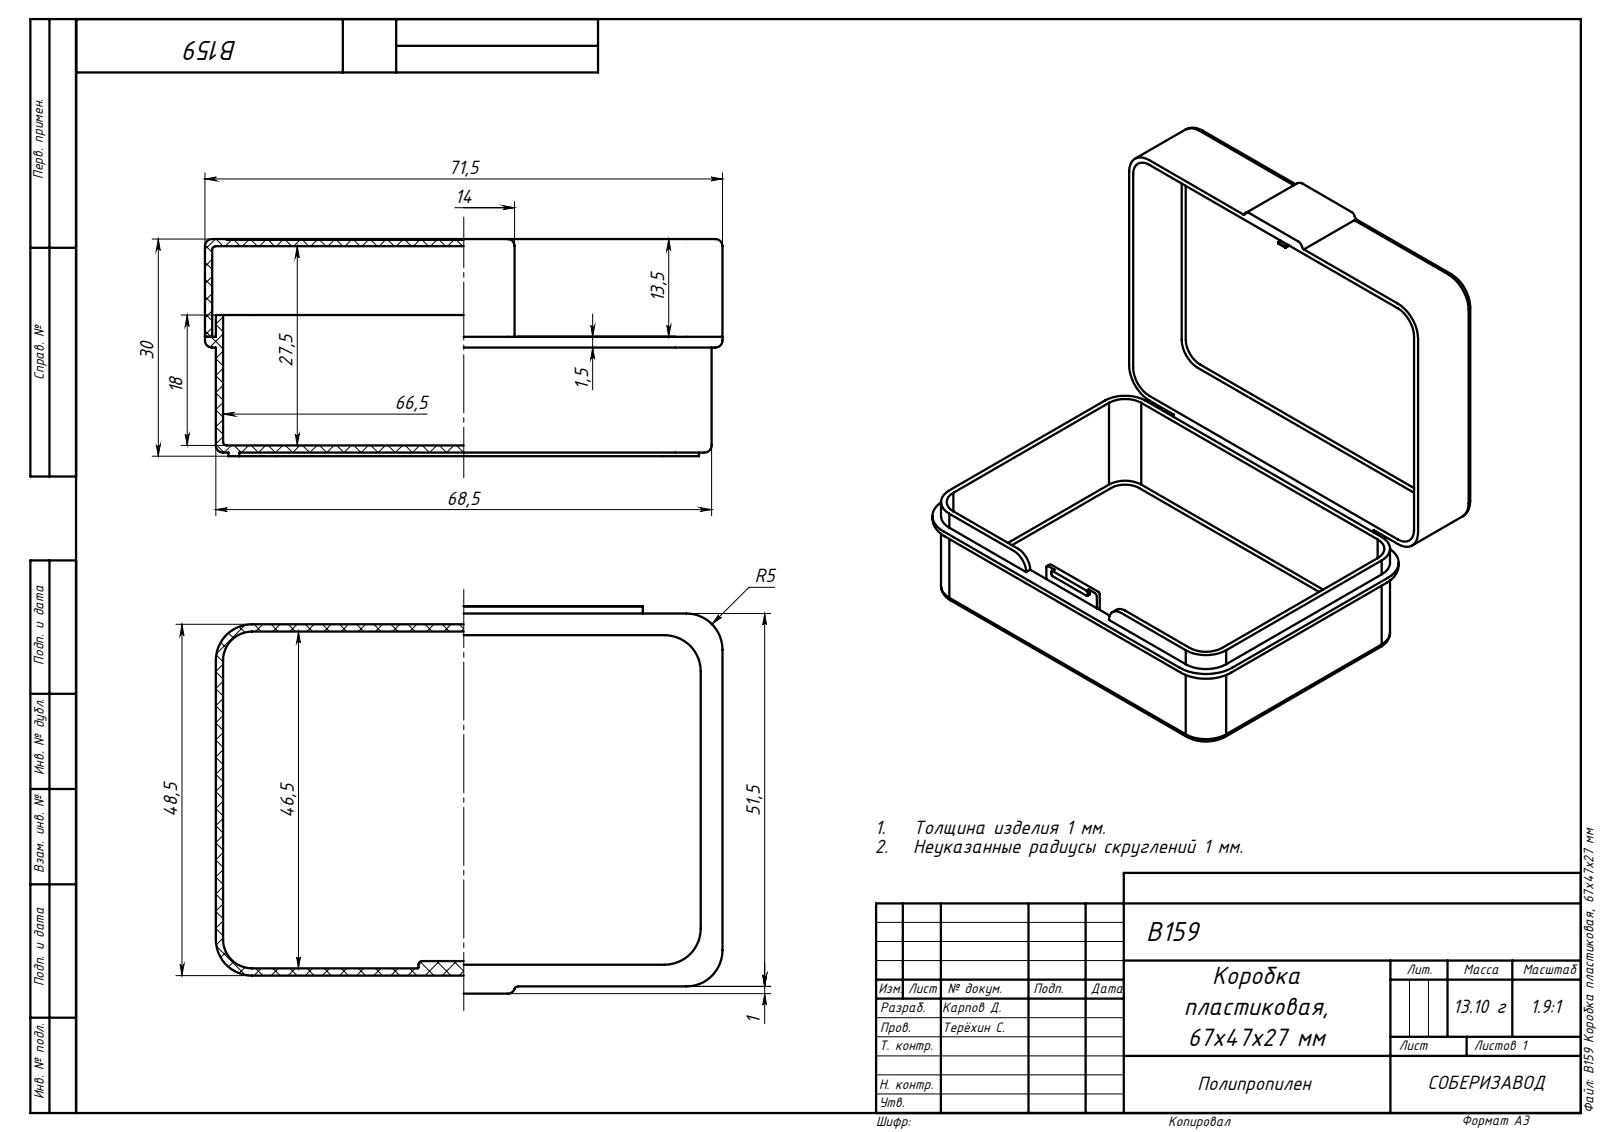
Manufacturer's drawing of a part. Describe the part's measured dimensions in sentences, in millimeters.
The part is named "B159 Емкость; B159 Крышка; B159 Коробка пластиковая, 67x47x27 мм". Its 3-D file was written by "SolidWorks 2020 (AUTOMOTIVE_DESIGN)". It is 2 solids with 193 faces: 78 planar, 85 cylindrical and 30 other. Overall it measures 71.5 by 53.5 by 30 millimeters. Its volume is 14 569 cubic millimeters and its surface area 29 026 square millimeters. Partial cylindrical surfaces (rounded edges, fillets, slot ends): 20 of radius 5, 15 of radius 0.5, 15 of radius 1, 10 of radius 0.1, 8 of radius 4, 4 of radius 0.3, 4 of radius 6.5, 2 of radius 3. The main face-to-face distances are 1, 1.5, 28.5, 27.5, 28.4, 0.9, 0.5, 49, 2.5, 29.4.
